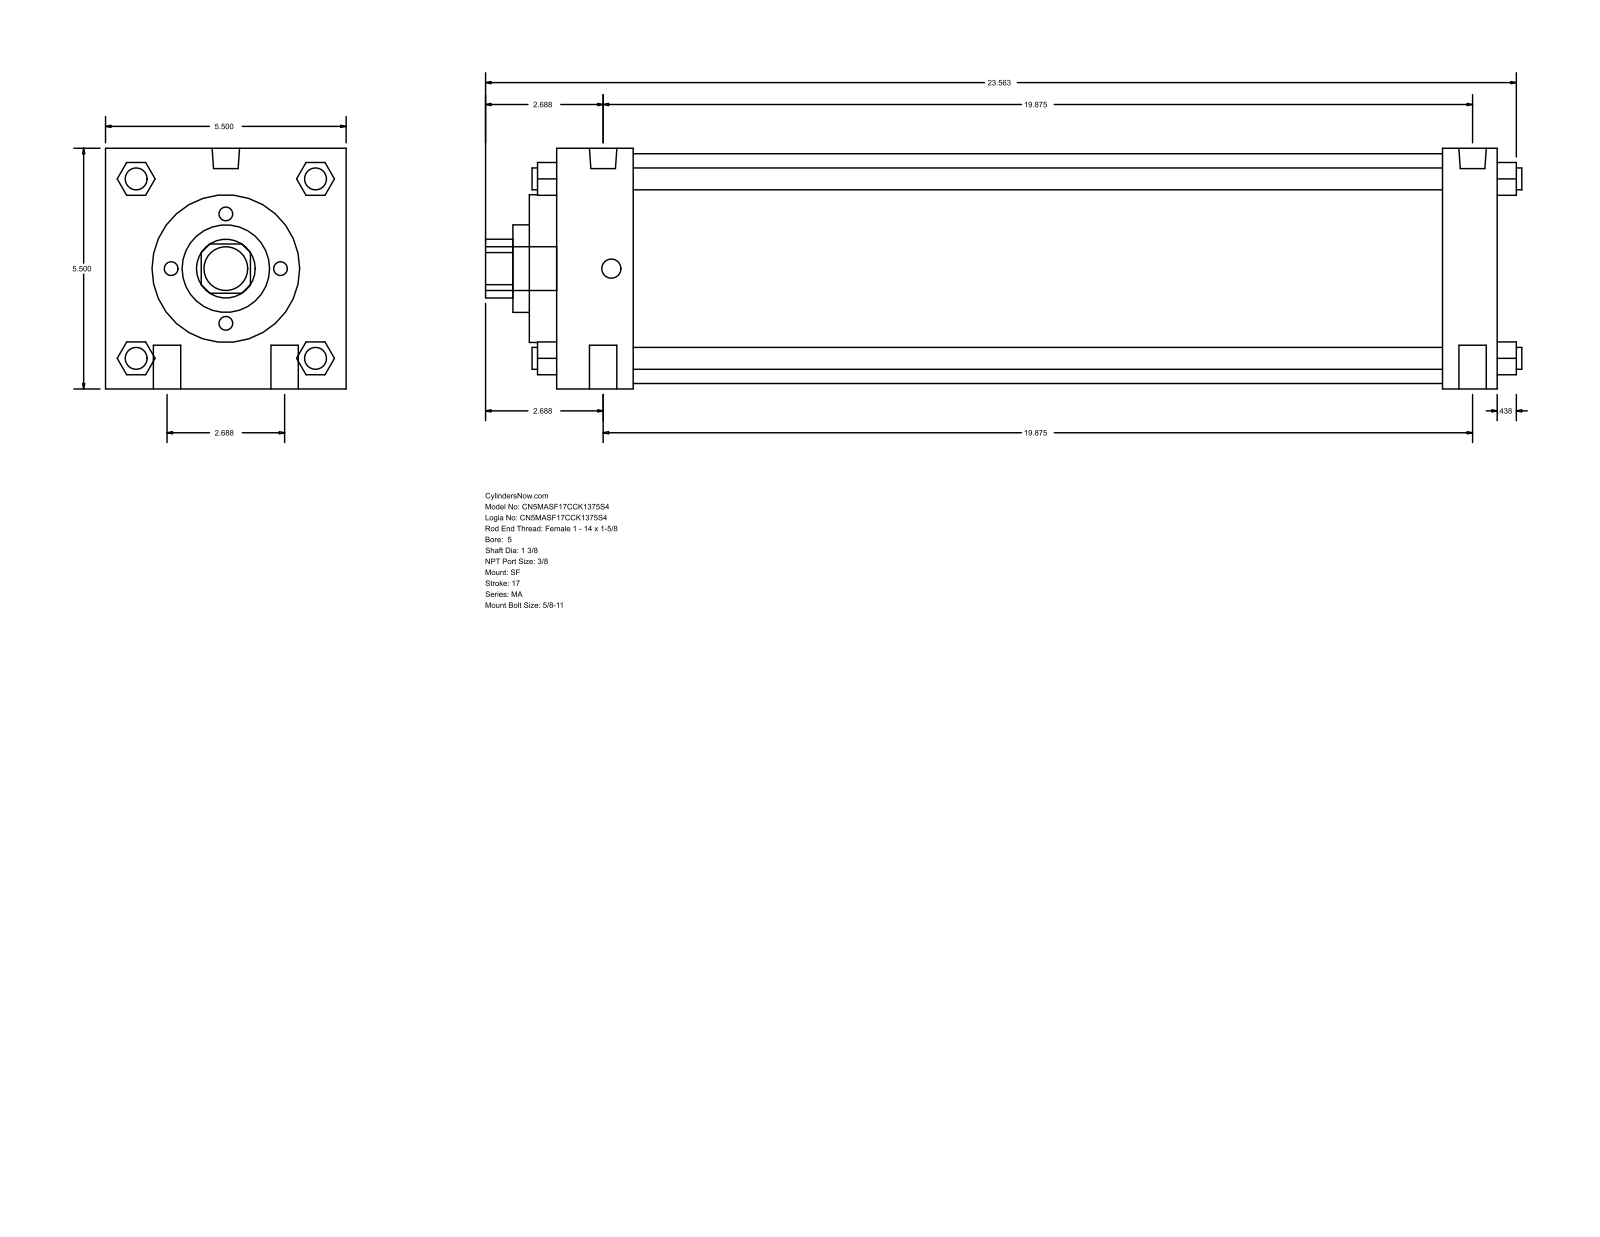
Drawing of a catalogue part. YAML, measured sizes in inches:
part_name: "MA_SF__0500_1.375"
step_written_by: "GSSL Pune (CONFIG_CONTROL_DESIGN)"
units: inches
bodies: {solids: 0, faces: 126, planar: 95, cylindrical: 31, other: 0}
overall_size: [23.687, 5.5, 5.5]
round_holes:
  - {diameter: 1.375, count: 1}
  - {diameter: 2, count: 1}
  - {diameter: 3.375, count: 1}
  - {diameter: 5.25, count: 1}
round_bosses_or_shafts:
  - {diameter: 0.625, count: 4}
  - {diameter: 0.5, count: 4}
  - {diameter: 0.627, count: 2}
  - {diameter: 0.437, count: 2}
  - {diameter: 1, count: 1}
partial_cylinders:
  - {radius: 0.672, count: 1}
face_to_face_distances: [5.5, 21.5, 1.75, 20.25, 18.5, 19.75, 1.25, 0.625, 2.375, 20.875]
